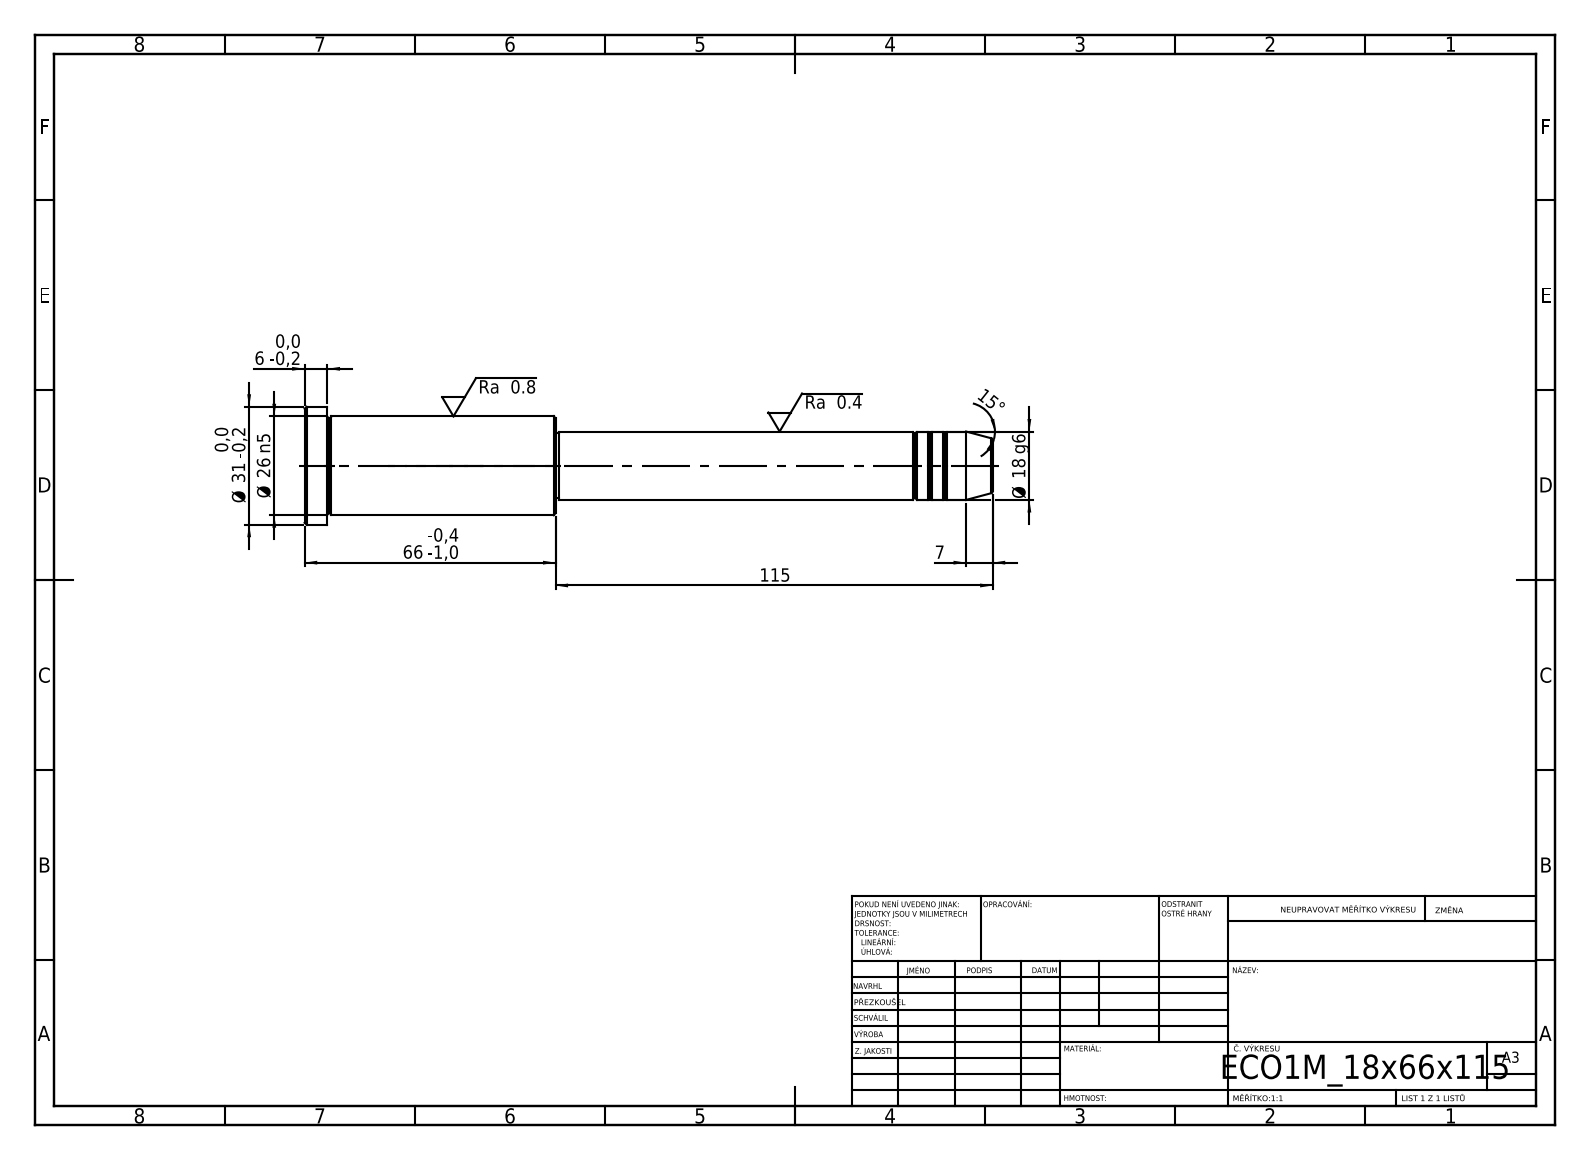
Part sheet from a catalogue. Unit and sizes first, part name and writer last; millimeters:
Units: millimetres
Overall size (bounding box): 181 × 31 × 31
Round bosses / shafts (diameter × count): ⌀31 ×1, ⌀26 ×1, ⌀18 ×1, ⌀17 ×1
Main face-to-face distances: 66, 60, 6, 115, 175, 181, 114, 1, 61, 67
Volume: 65 155 mm³ · Surface area: 13 499 mm²
Bodies: 1 solid, 43 faces (5 planar, 14 cylindrical, 24 other)
STEP written by: SolidWorks 2019 (CONFIG_CONTROL_DESIGN)
